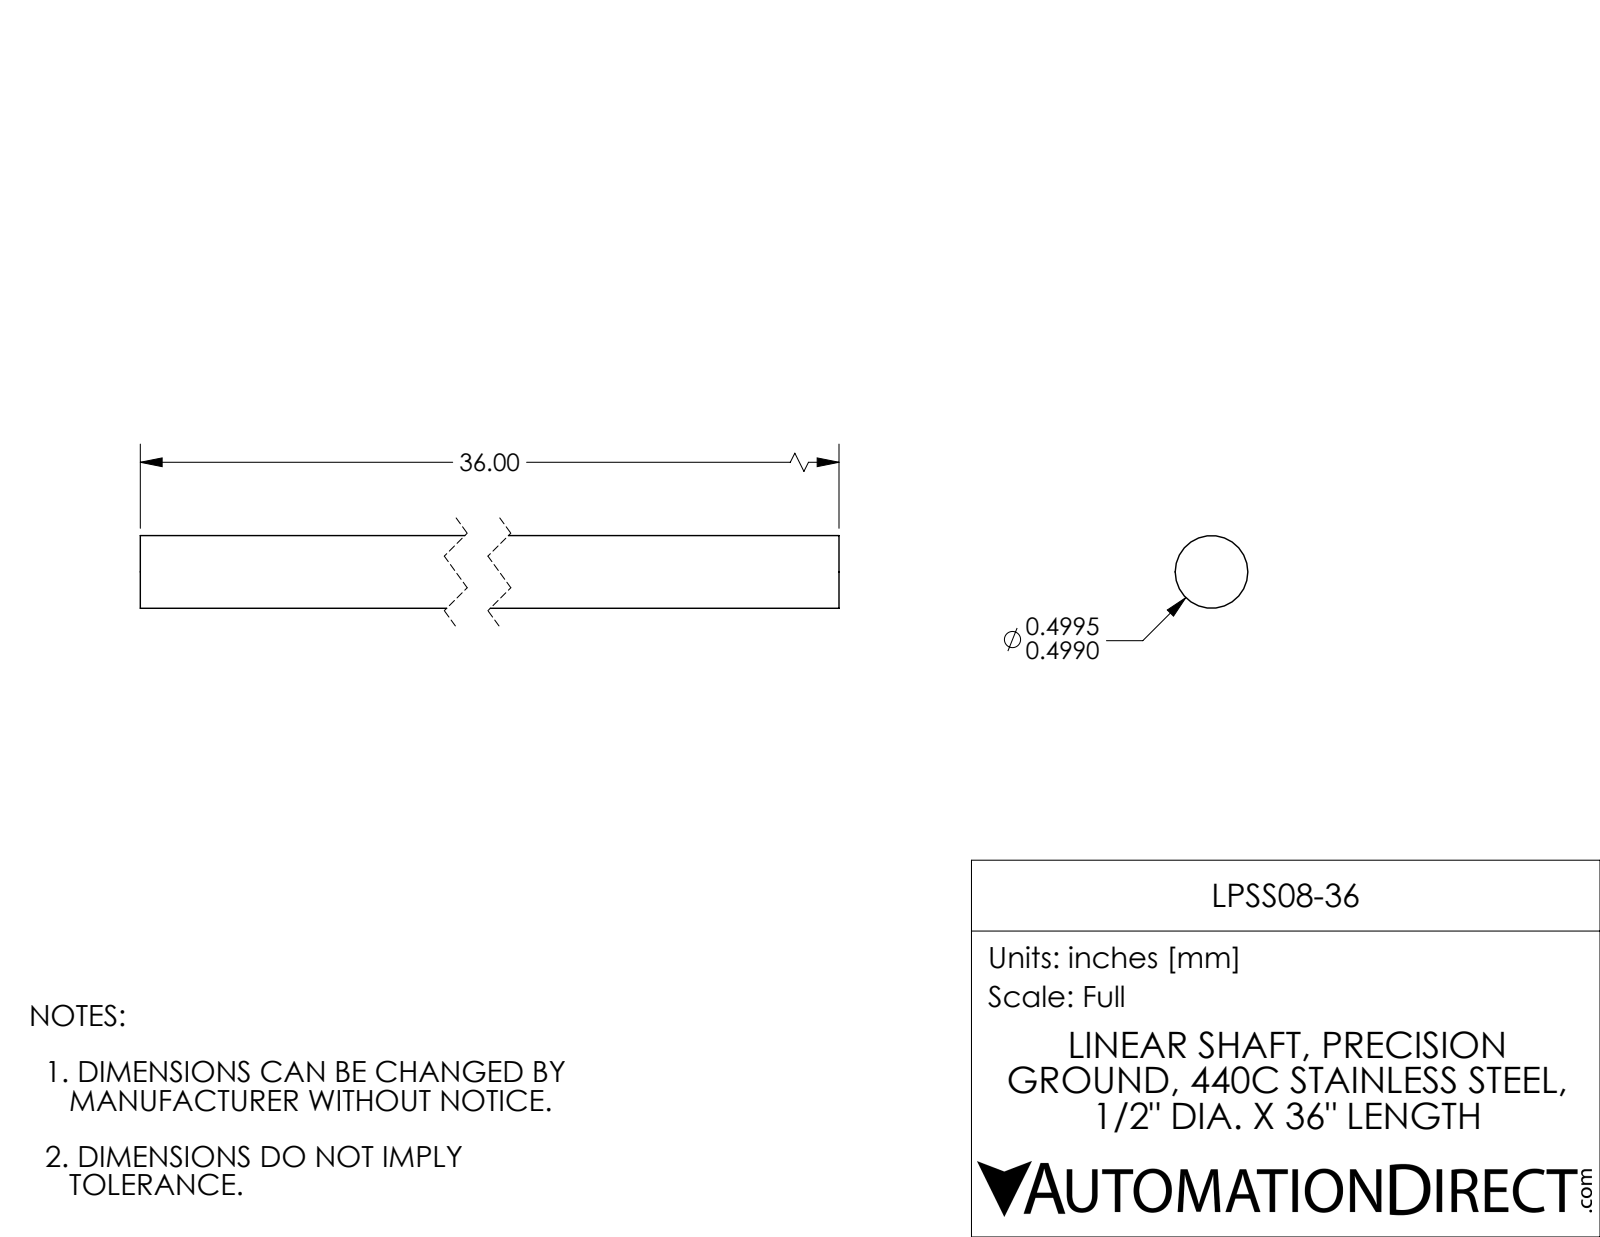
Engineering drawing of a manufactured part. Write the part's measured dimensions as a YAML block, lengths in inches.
part_name: "LPSS08-36"
step_written_by: "SolidWorks 2017 (AUTOMOTIVE_DESIGN)"
units: inches
bodies: {solids: 1, faces: 4, planar: 2, cylindrical: 2, other: 0}
overall_size: [36, 0.499, 0.499]
volume: 7.054
surface_area: 56.88
round_bosses_or_shafts:
  - {diameter: 0.5, count: 1}
face_to_face_distances: [36]
